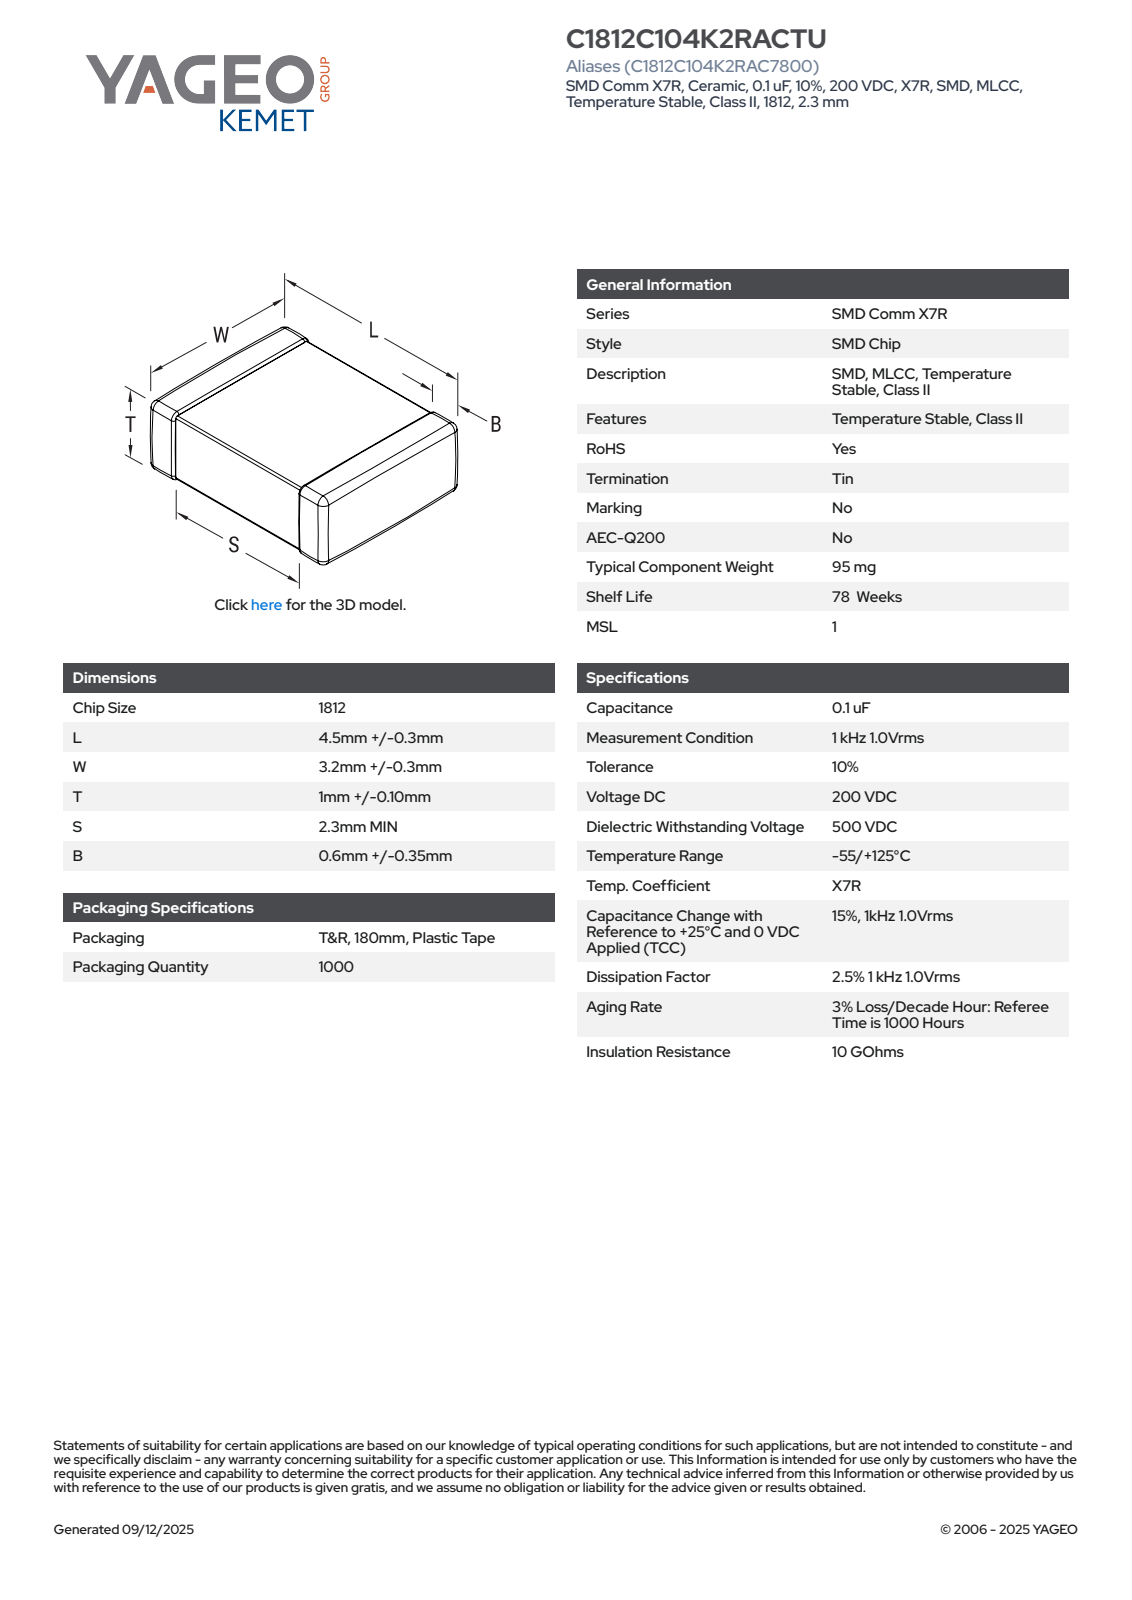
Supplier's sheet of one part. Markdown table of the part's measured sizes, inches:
| quantity | value |
| --- | --- |
| part name | CCS_CCSTD_1812_L4.8W3.5T1.1B0.6 |
| STEP written by | SolidWorks 2021 (AUTOMOTIVE_DESIGN) |
| units | inches |
| bodies | 4 solids, 129 faces (71 planar, 42 cylindrical, 16 other) |
| overall size | 0.189 × 0.138 × 0.043 |
| volume | 0.001 in³ |
| surface area | 0.079 in² |
| main face-to-face distances | 0.041, 0.038, 0.043, 0.189, 0.135, 0.132, 0.138, 0.082, 0.107, 0.102 |
